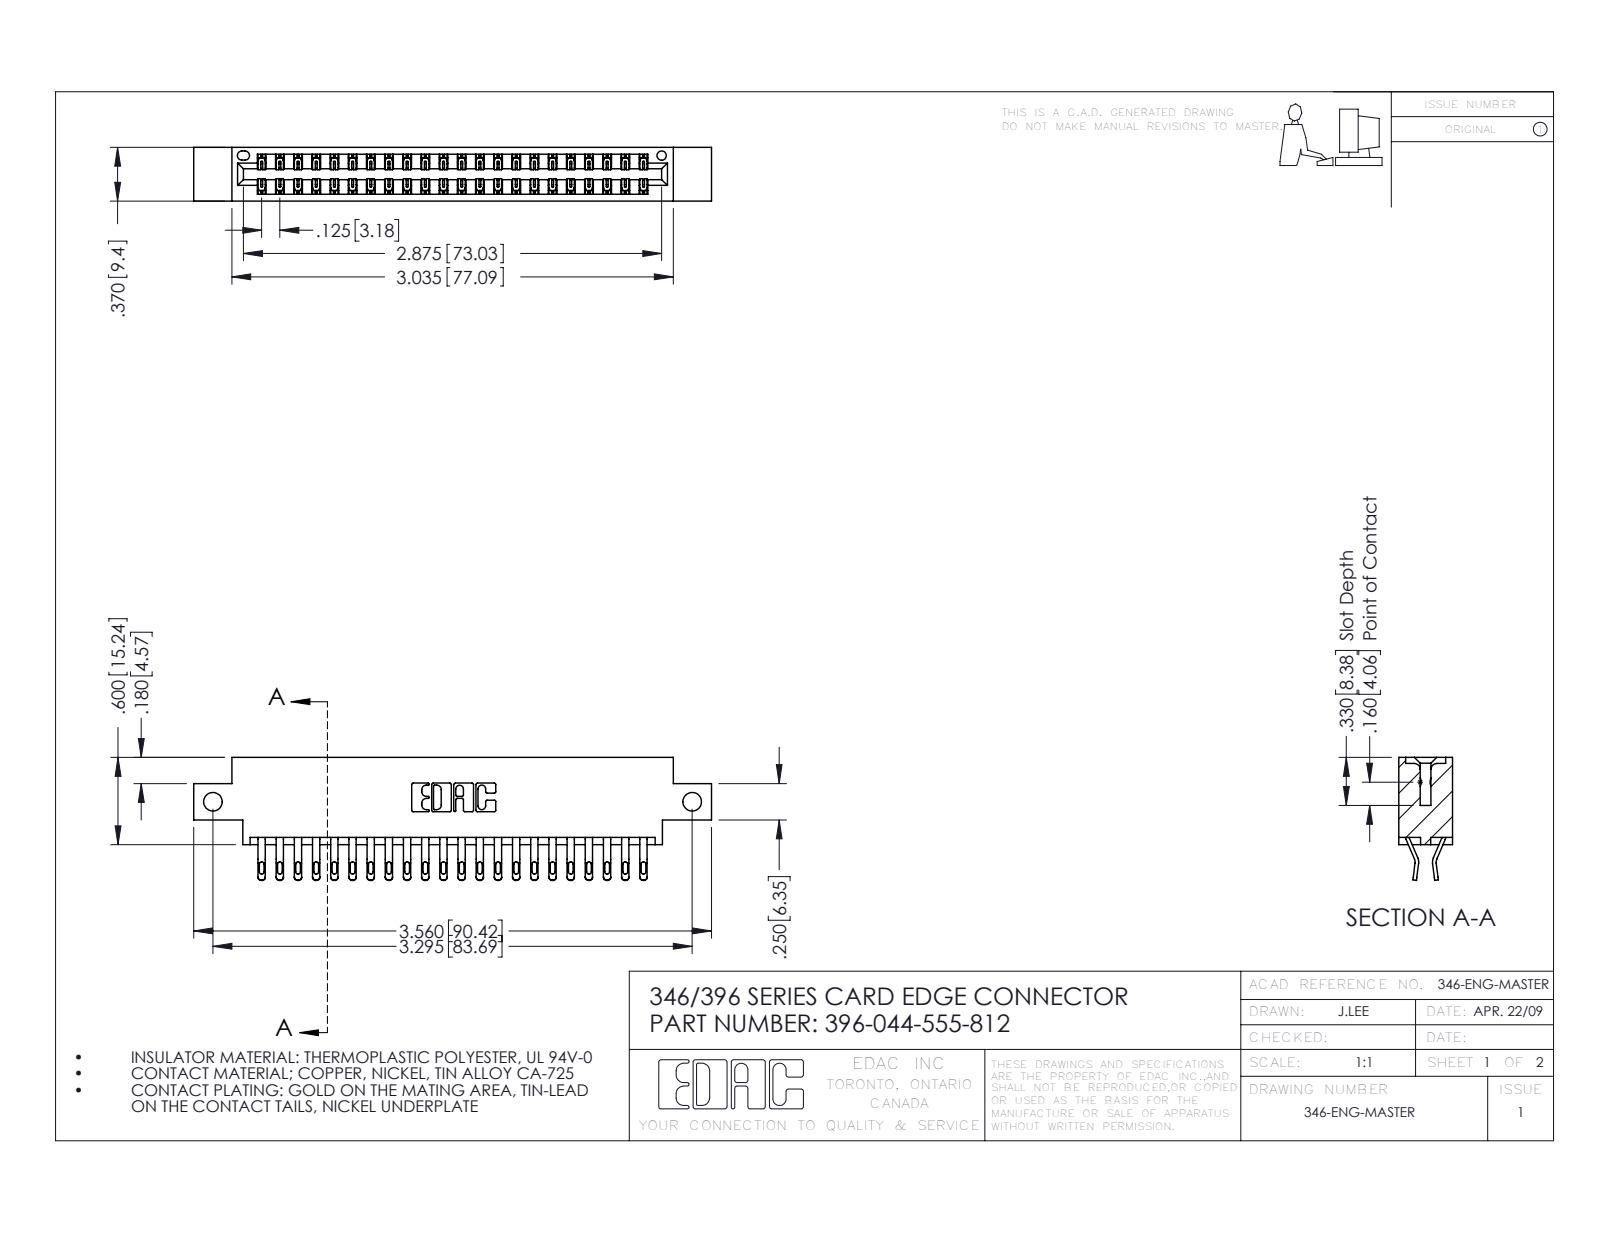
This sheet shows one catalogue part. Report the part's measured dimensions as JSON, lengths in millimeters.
{"part_name": "345-292-001_555 Tail; 396-044-555-812; 346 Part_0.170 Offset - Side Mount", "step_written_by": "SolidWorks 2016 (CONFIG_CONTROL_DESIGN)", "units": "millimeters", "bodies": {"solids": 45, "faces": 2678, "planar": 1532, "cylindrical": 1146, "other": 0}, "overall_size": [90.4, 21.5, 9.4], "volume_mm3": 8550, "surface_area_mm2": 11940, "round_holes": [[3.3, 2], [1.6, 1]], "partial_cylinders_radius": [[0.4, 88], [0.5, 88], [0.2, 66], [0.3, 22], [0.2, 6], [0.8, 6], [0.7, 3], [0.3, 2]], "face_to_face_distances": [1.2, 8.2, 9.4, 6.4, 0.6, 1.8, 7.6, 7, 3.8, 5.6], "hole_center_spacings": [83.7]}
